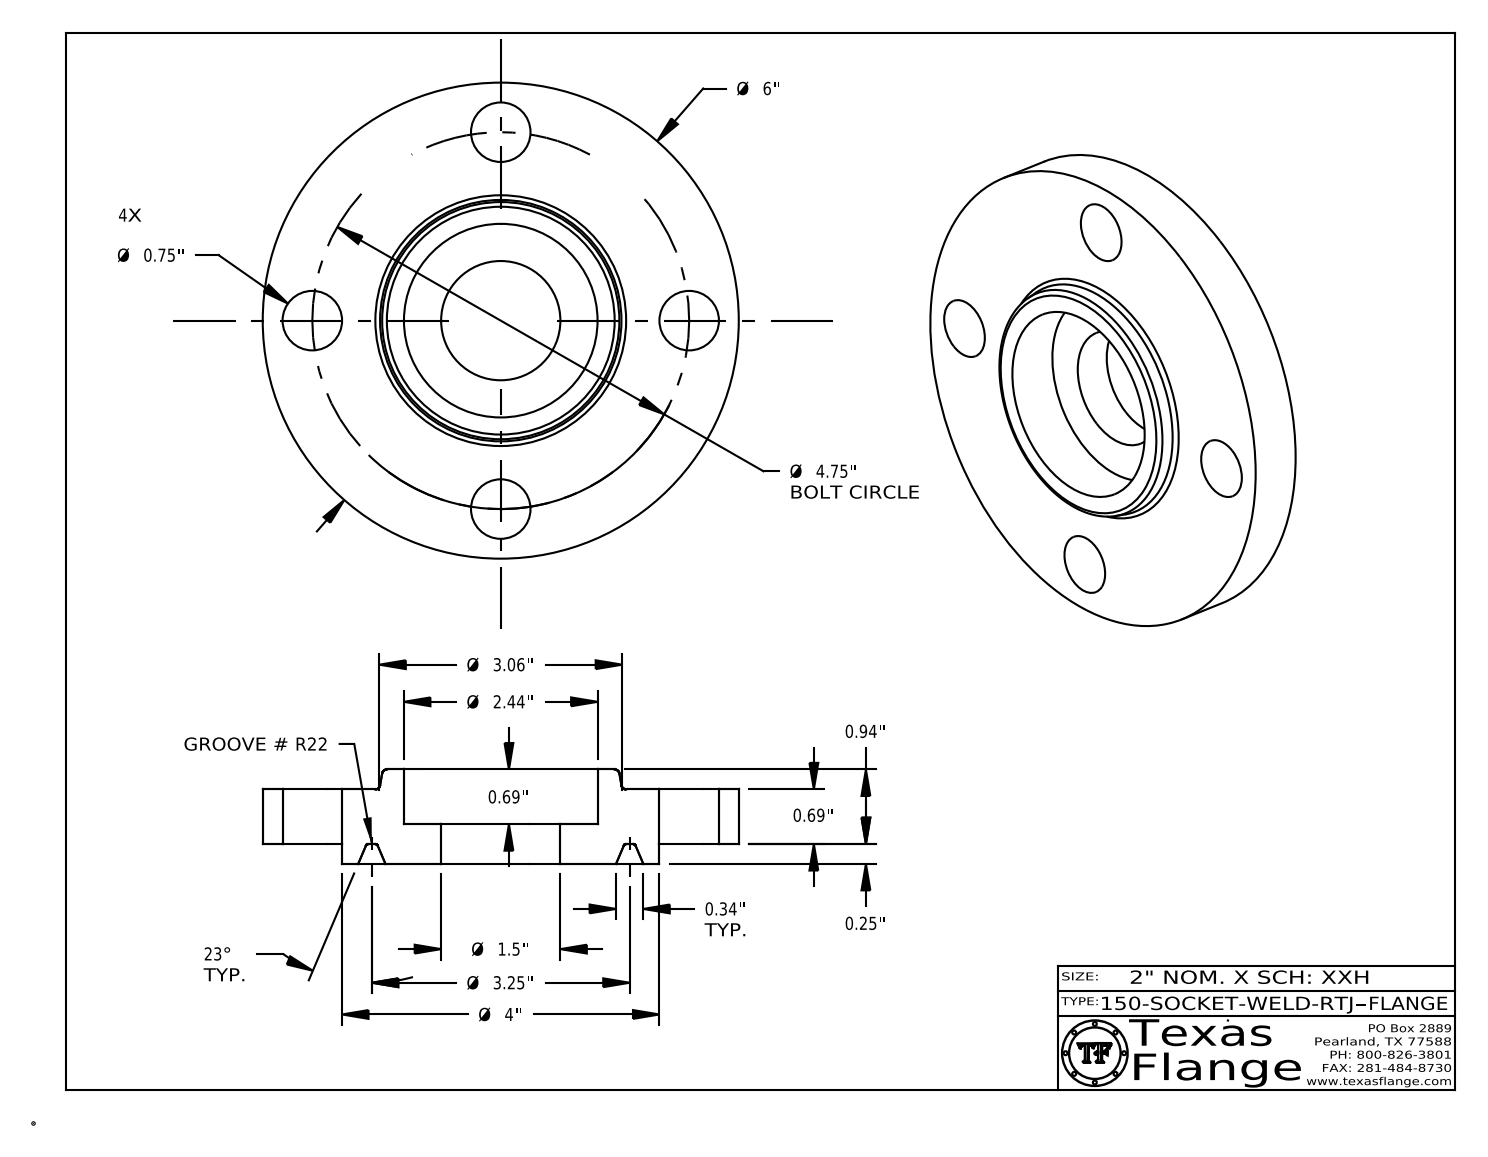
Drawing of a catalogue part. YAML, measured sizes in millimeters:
part_name: "150-SOCKET-WELD-RTJ"
step_written_by: "CATIA V5 STEP AP214 (AUTOMOTIVE_DESIGN)"
units: millimeters
bodies: {solids: 1, faces: 422, planar: 372, cylindrical: 36, other: 14}
overall_size: [152.4, 152.4, 30.2]
volume: 303200
surface_area: 54720
round_holes:
  - {diameter: 19.1, count: 4}
  - {diameter: 12.6, count: 1}
  - {diameter: 38.2, count: 1}
  - {diameter: 62, count: 1}
round_bosses_or_shafts:
  - {diameter: 0.8, count: 8}
  - {diameter: 152.4, count: 1}
  - {diameter: 101.6, count: 1}
  - {diameter: 9.9, count: 1}
face_to_face_distances: [17.5, 6.4, 23.9, 12.7, 11.2, 30.2, 23.5, 17.1, 10.8, 0.4]
hole_center_spacings: [60.3, 85.3, 46.2, 111.5, 120.7]
